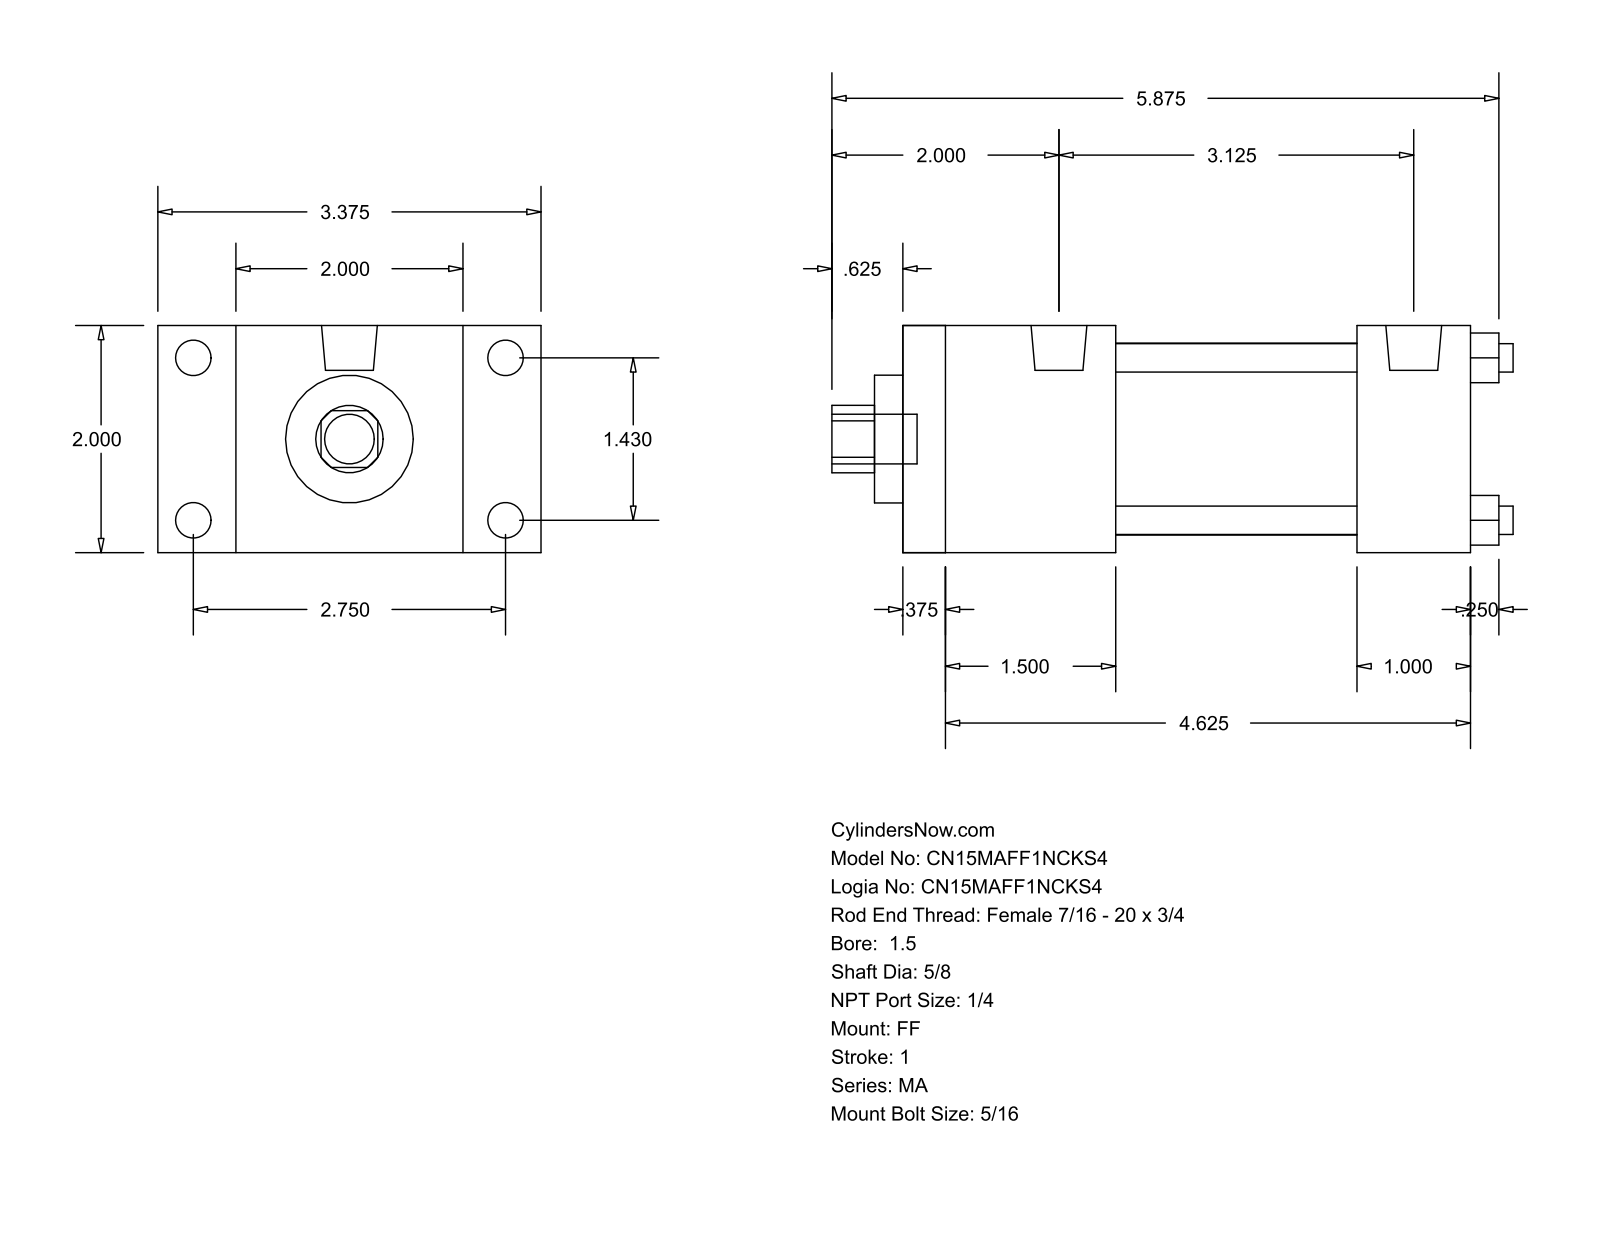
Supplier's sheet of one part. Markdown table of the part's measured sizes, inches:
| quantity | value |
| --- | --- |
| part name | MA_FF__0150_0.625 |
| STEP written by | GSSL Pune (CONFIG_CONTROL_DESIGN) |
| units | inches |
| bodies | 0 solids, 92 faces (64 planar, 28 cylindrical, 0 other) |
| overall size | 6 × 3.375 × 2 |
| round holes (diameter × count) | 0.25 × 4, 0.625 × 1, 1.125 × 1, 1.69 × 1 |
| round bosses / shafts (diameter × count) | 0.313 × 8, 0.492 × 2, 0.437 × 1 |
| partial cylindrical surfaces (radius × count) | 0.297 × 1 |
| main face-to-face distances | 2, 5, 0.375, 4.625, 2.125, 1.875, 4, 1.5, 3.625, 3.125 |
| hole center spacings | 1.011, 1.43, 2.022 |
